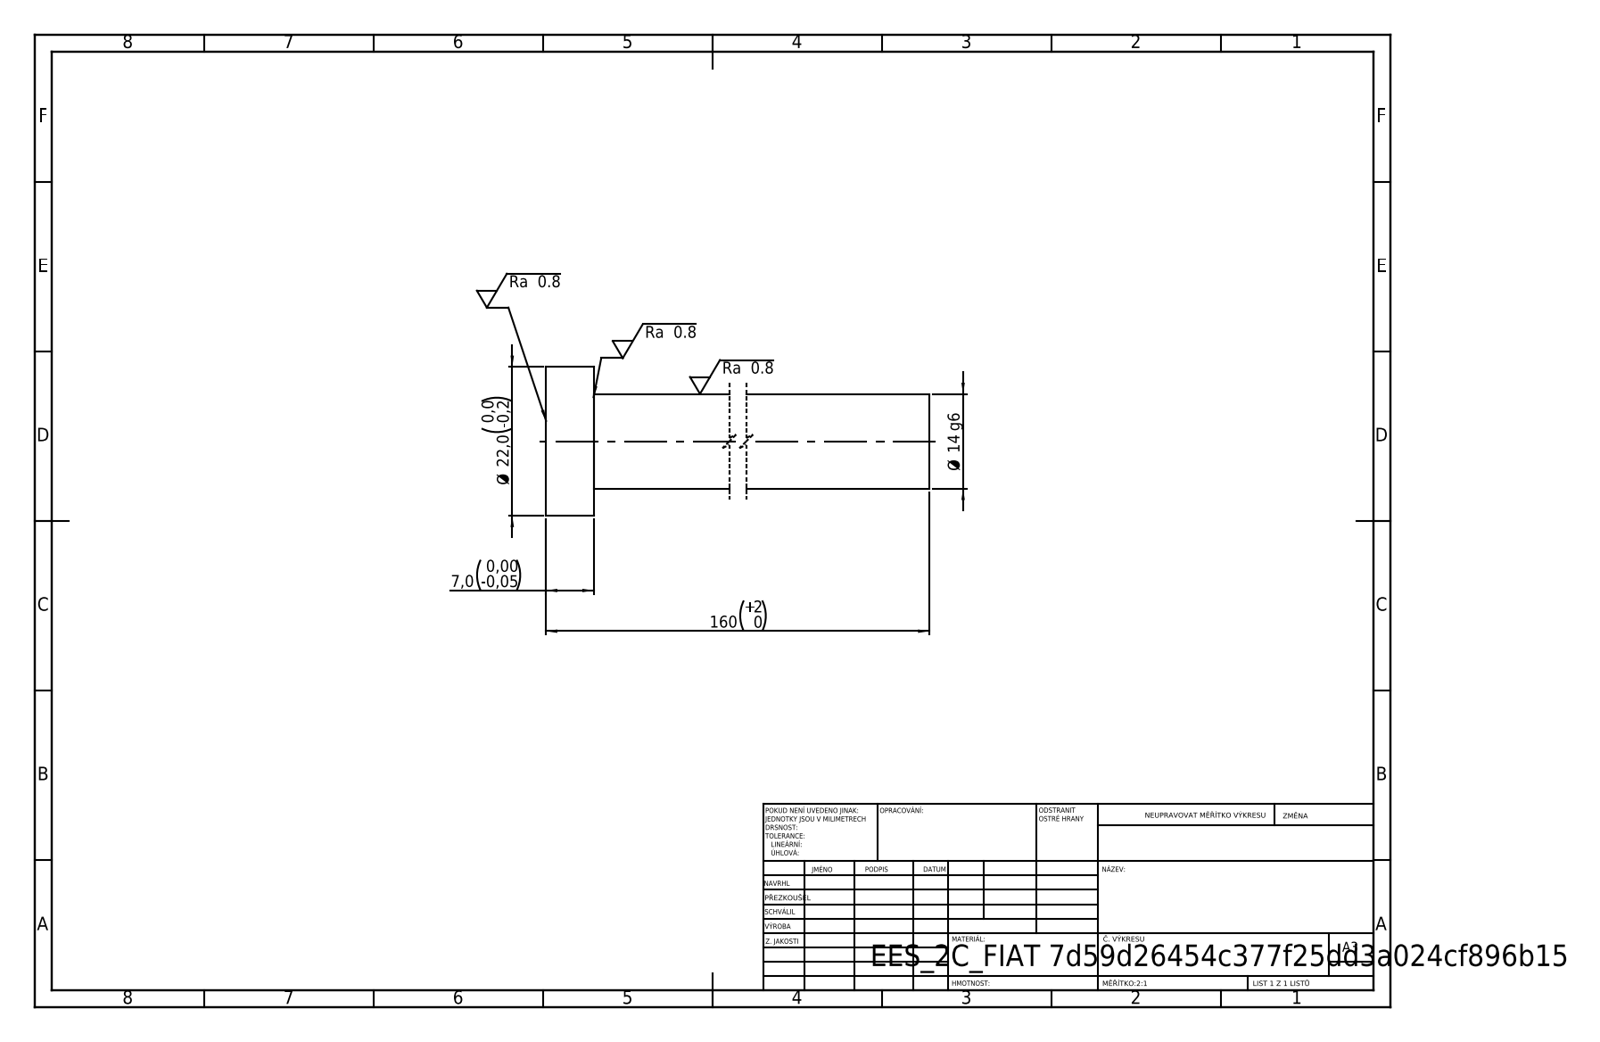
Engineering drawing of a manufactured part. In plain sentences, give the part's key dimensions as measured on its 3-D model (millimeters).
Its 3-D file was written by "SolidWorks 2019 (CONFIG_CONTROL_DESIGN)". It is 1 solid with 7 faces: 3 planar, 4 cylindrical and 0 other. Overall it measures 160 by 22 by 22 millimeters. Its volume is 26 213 cubic millimeters and its surface area 7 973 square millimeters. Round bosses or shafts: 1 of diameter 22, 1 of diameter 14. The main face-to-face distances are 7, 160, 153.
